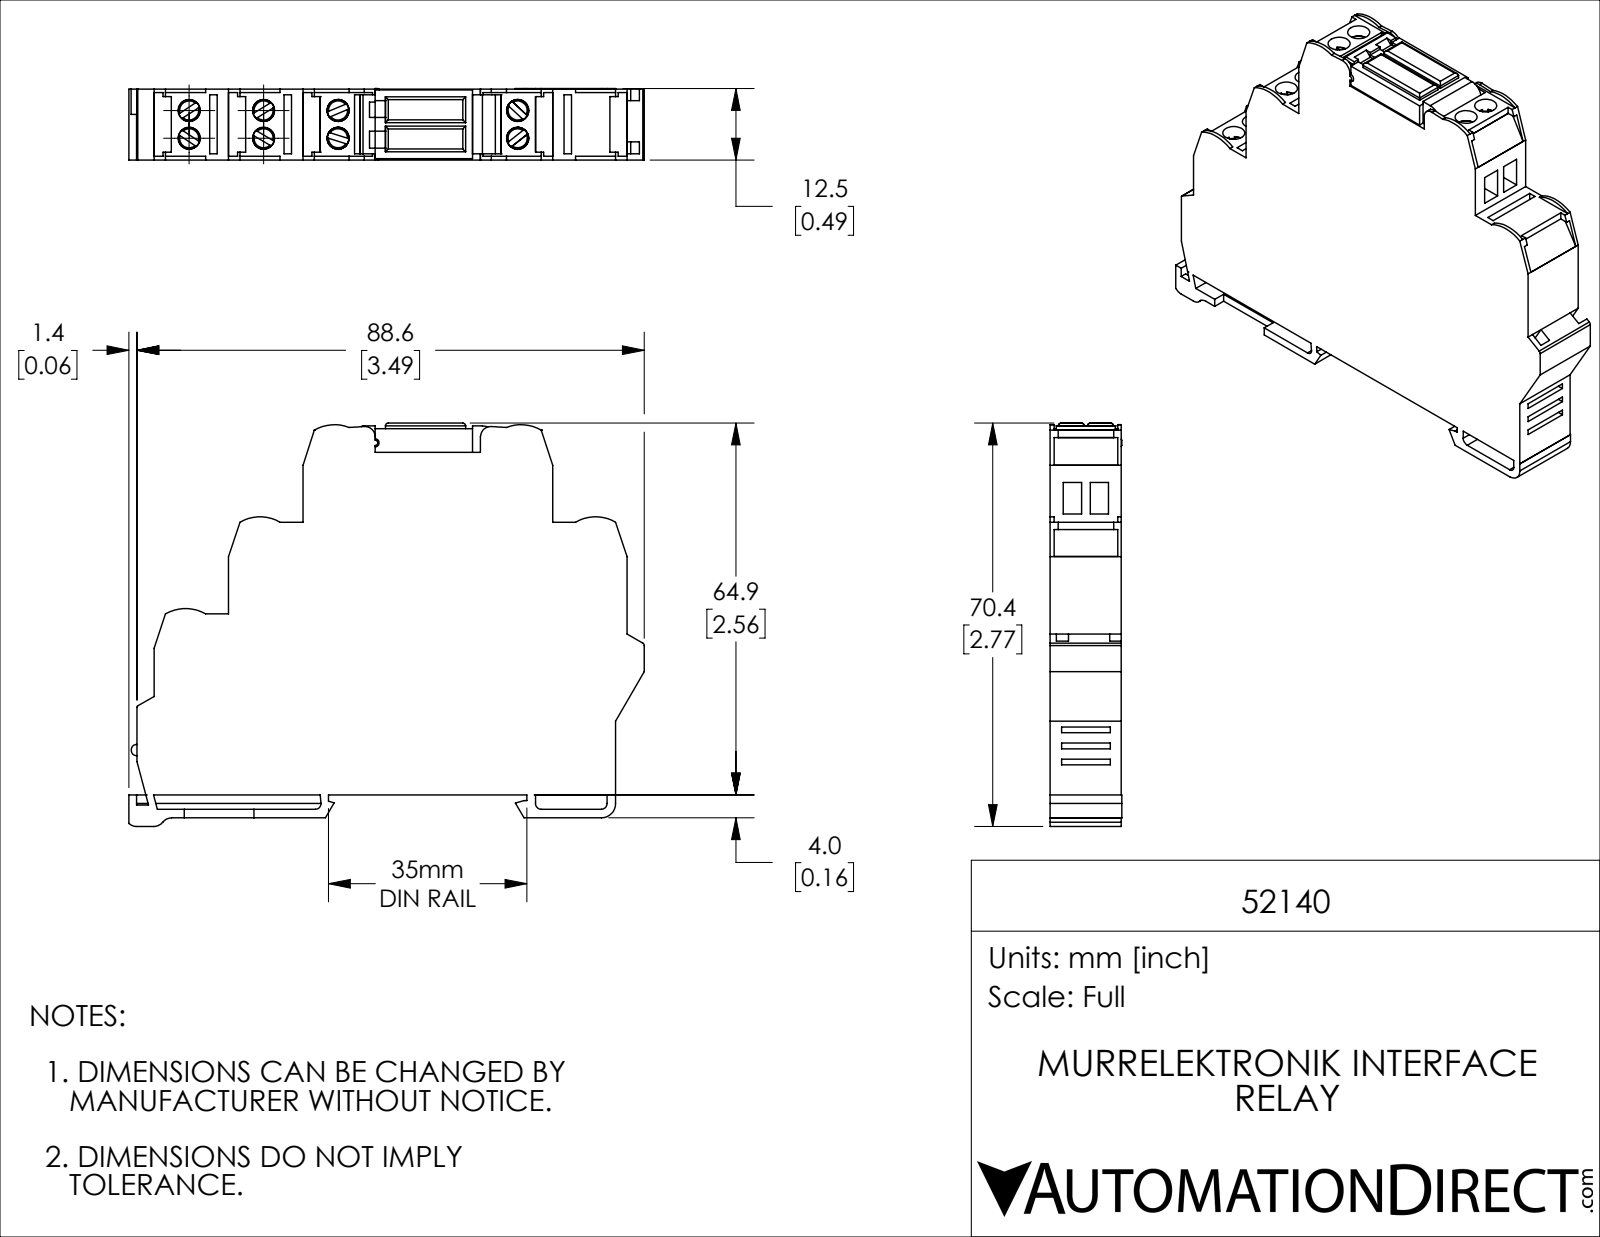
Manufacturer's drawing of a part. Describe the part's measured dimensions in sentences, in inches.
The part is named "52140". Its 3-D file was written by "SolidWorks 2019 (CONFIG_CONTROL_DESIGN)". It is 1 solid with 419 faces: 315 planar, 78 cylindrical and 26 other. Overall it measures 3.543 by 2.772 by 0.492 inches. Its volume is 3.294 cubic inches and its surface area 27.11 square inches. Round holes: 8 of diameter 0.152. Round bosses or shafts: 8 of diameter 0.148. Partial cylindrical surfaces (rounded edges, fillets, slot ends): 9 of radius 0.02, 5 of radius 0.276, 4 of radius 0.039, 3 of radius 0.079, 2 of radius 0.028, 2 of radius 0.071, 2 of radius 0.089, 1 of radius 0.012. The main face-to-face distances are 0.488, 0.059, 0.157, 0.039, 0.098, 0.217, 0.185, 0.126, 0.207, 1.874. The hole center spacings are 0.512, 0.191, 0.546, 1.024, 1.041, 1.235, 1.249, 1.746.
